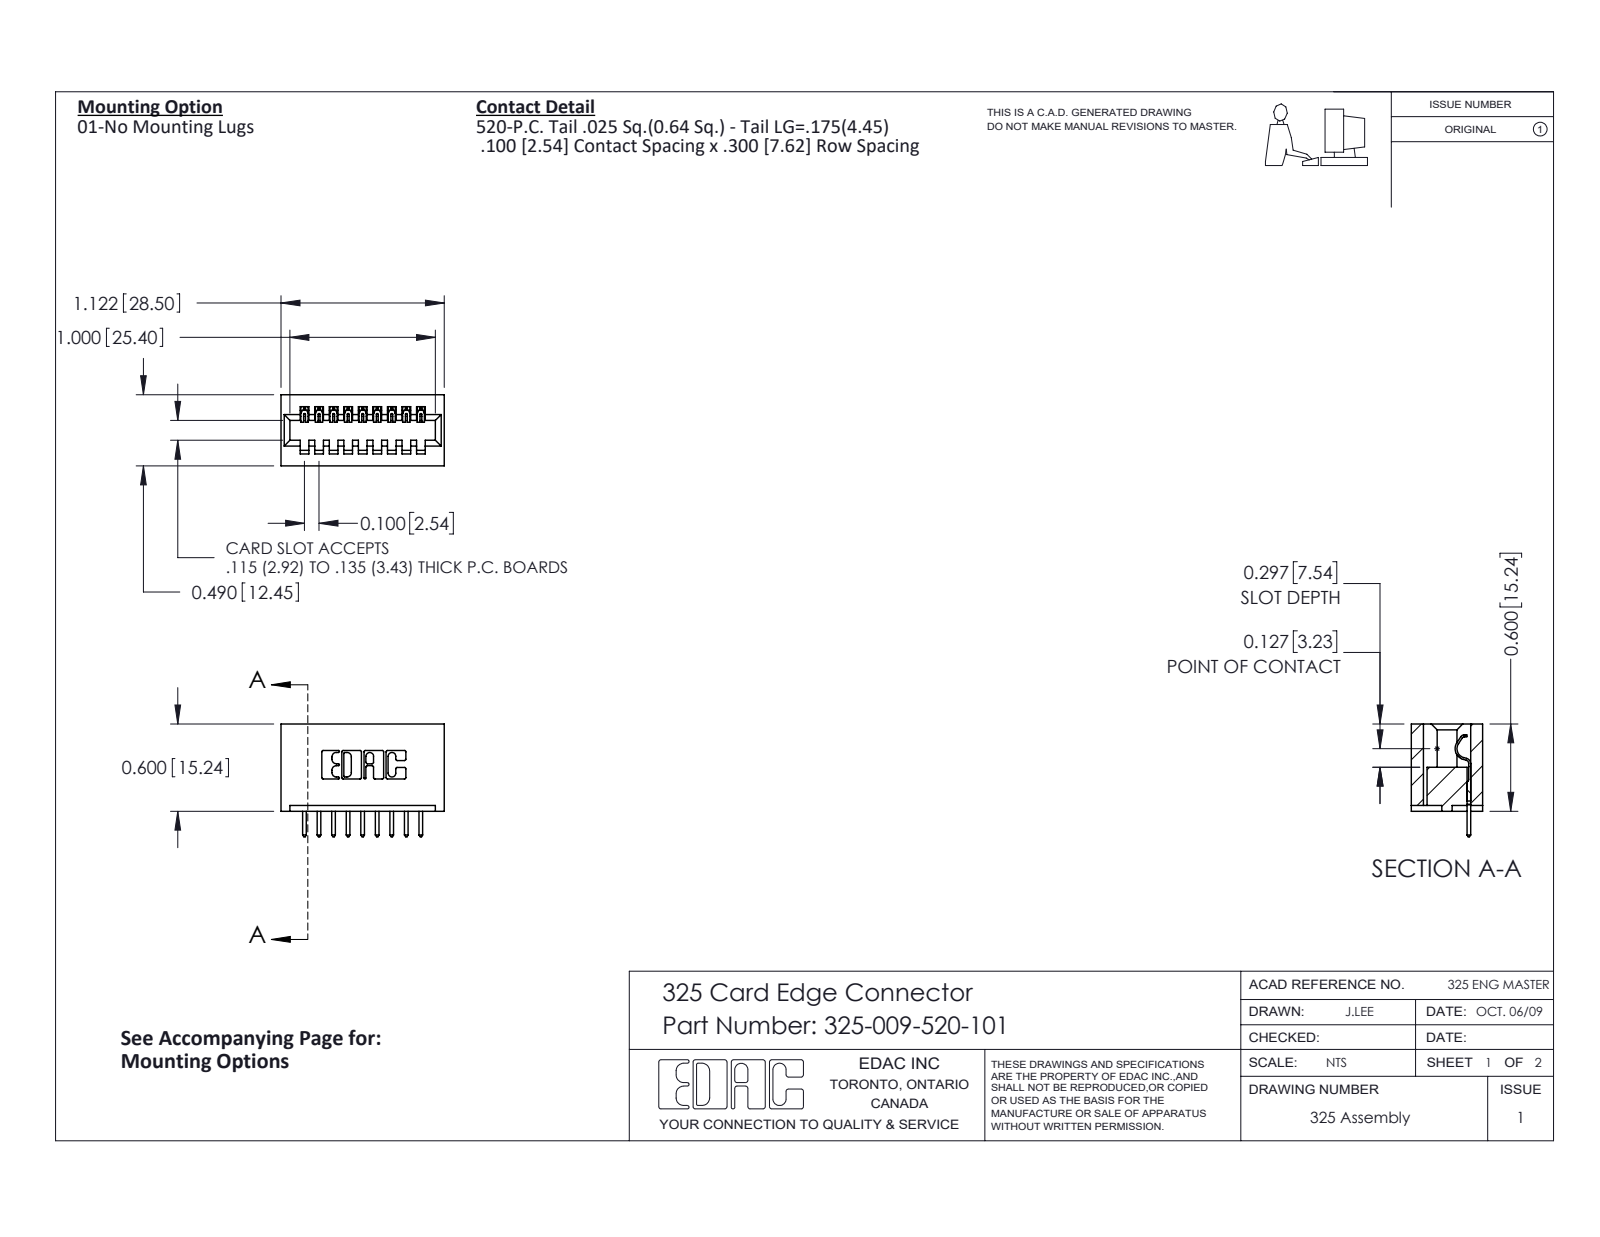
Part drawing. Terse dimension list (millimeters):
name: 325 Part_Lugless; 325-009-520-101; 325-292-001_325-293-120
written by: SolidWorks 2016 (CONFIG_CONTROL_DESIGN)
unit: mm
bodies: 10 solids, 628 faces (444 planar, 184 cylindrical, 0 other)
size: 28.5 × 19.7 × 12.4
volume: 3 900 mm³; area: 4 104 mm²
rounds: 22× R0.3, 18× R0.2, 18× R0.3, 6× R0.2, 6× R0.8, 3× R0.7, 1× R0.4, 1× R0.6
face distances: 7.6, 2.5, 5.1, 2.1, 10.3, 10.2, 1, 1.5, 12.4, 12.7
